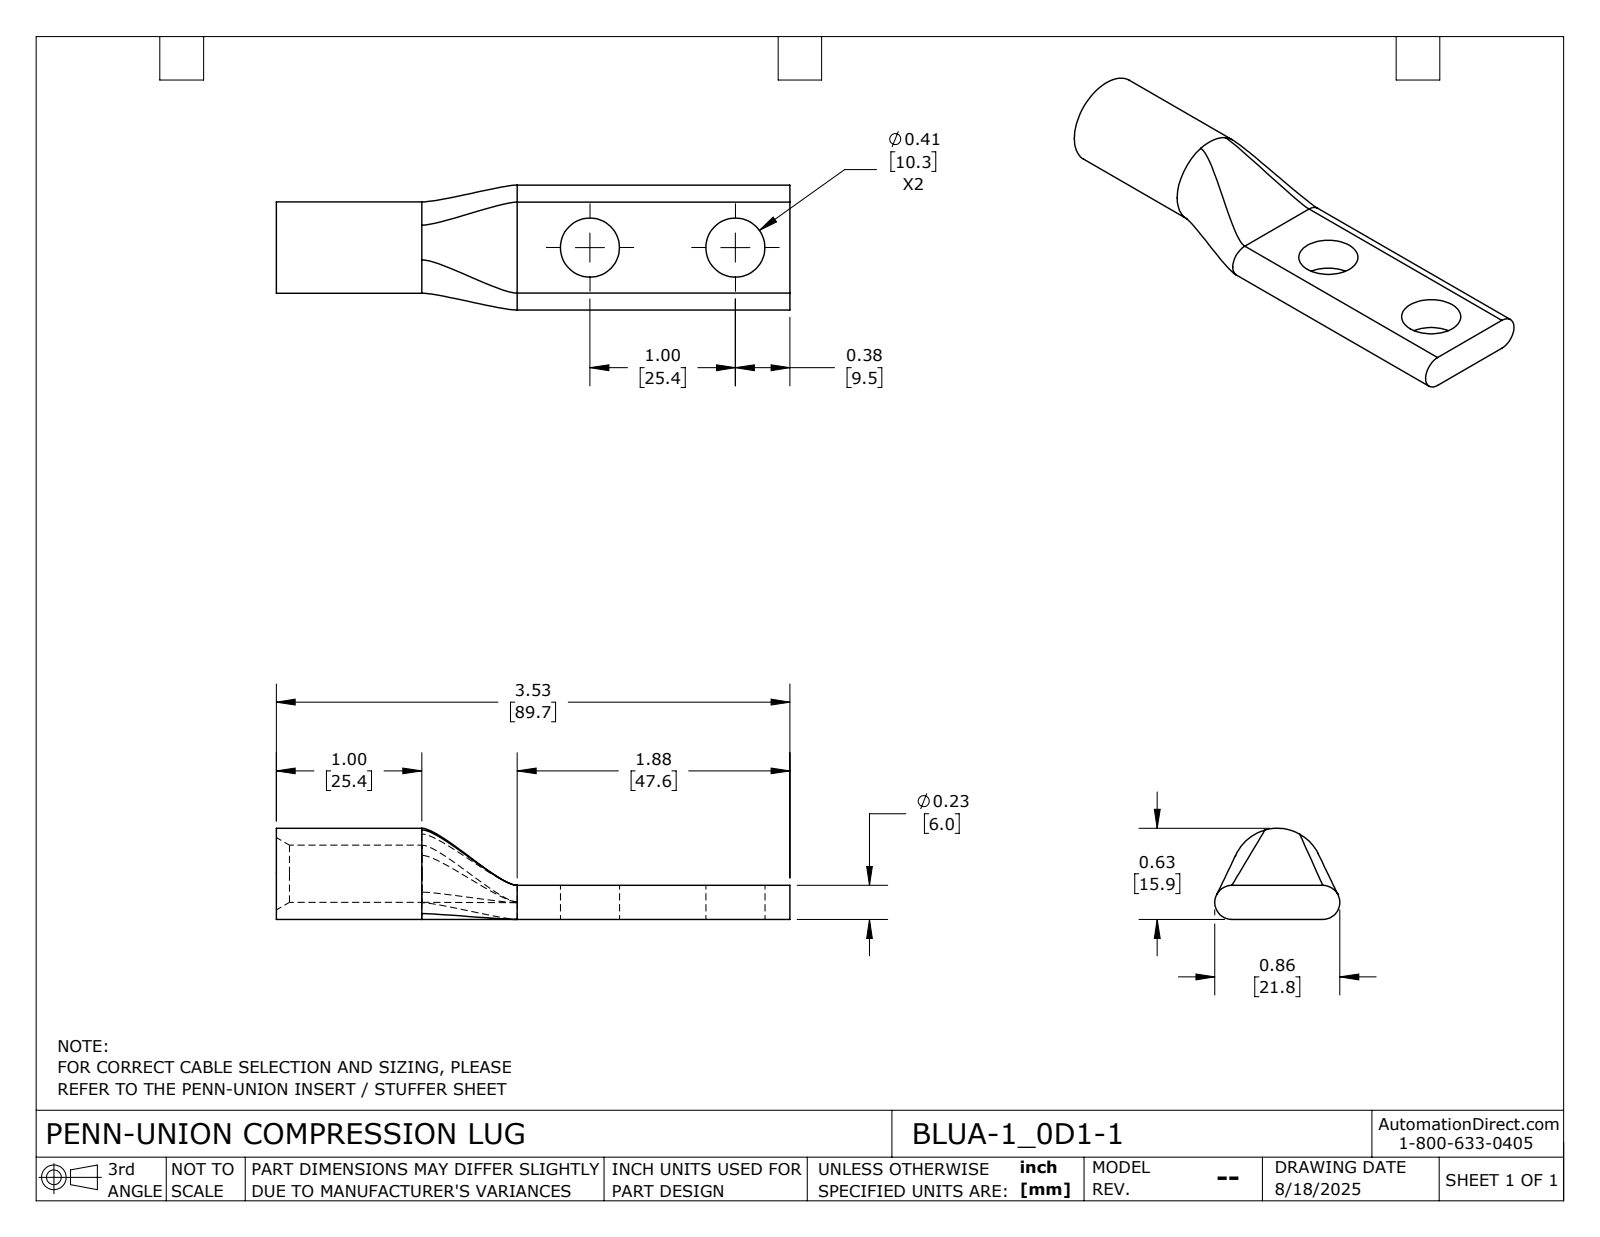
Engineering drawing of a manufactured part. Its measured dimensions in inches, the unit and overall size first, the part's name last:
Units: inches
Overall size (bounding box): 3.531 × 0.859 × 0.627
Round holes (diameter × count): ⌀0.406 ×2, ⌀0.393 ×1
Round bosses / shafts (diameter × count): ⌀0.627 ×1
Partial cylindrical surfaces — rounded edges, fillets, slot ends (radius × count): R0.117 ×2
Main face-to-face distances: 0.234, 3.531, 1.656, 1.875
Hole centre spacings: 1
Volume: 0.601 in³ · Surface area: 9.559 in²
Bodies: 1 solid, 26 faces (5 planar, 11 cylindrical, 10 other)
Part name (STEP PRODUCT): BLUA-1_0D1-1
STEP written by: SolidWorks 2024 (CONFIG_CONTROL_DESIGN)
